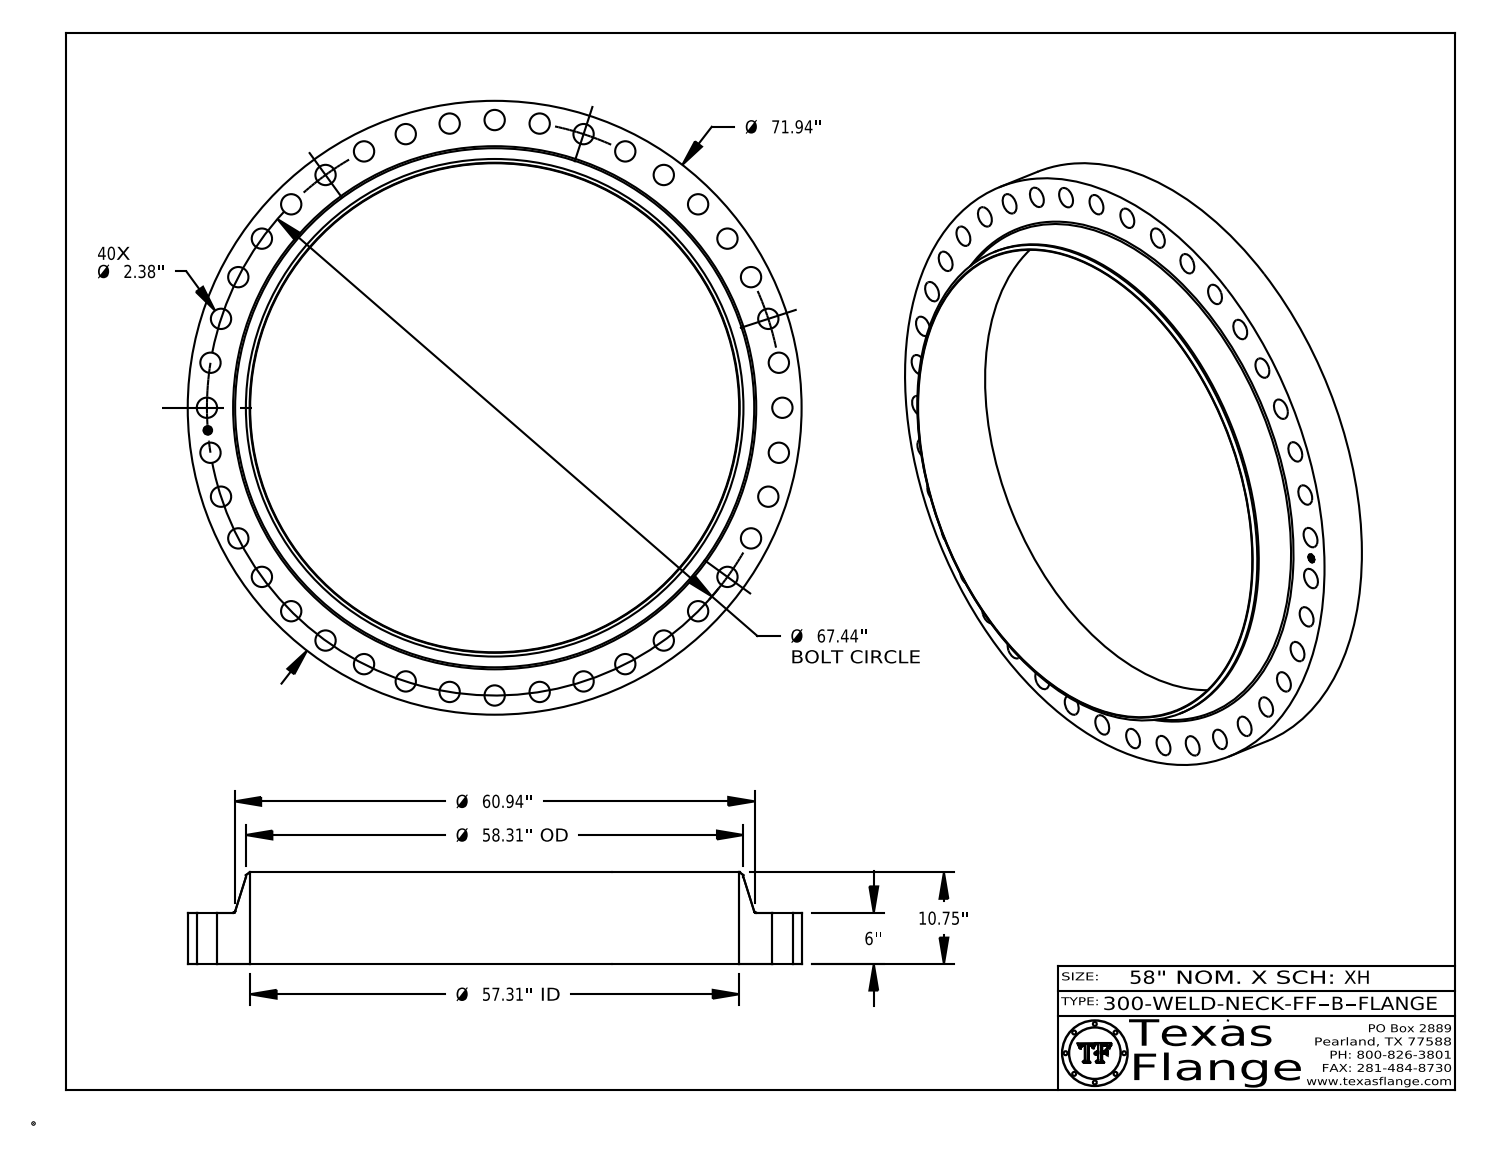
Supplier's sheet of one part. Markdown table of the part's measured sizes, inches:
| quantity | value |
| --- | --- |
| part name | 300-WELD-NECK-FF, Series B |
| STEP written by | CATIA V5 STEP AP214 (AUTOMOTIVE_DESIGN) |
| units | inches |
| bodies | 1 solid, 480 faces (368 planar, 106 cylindrical, 6 other) |
| overall size | 71.94 × 71.94 × 10.75 |
| volume | 8 773 in³ |
| surface area | 8 329 in² |
| round holes (diameter × count) | 2.38 × 40, 1 × 1, 57.31 × 1 |
| round bosses / shafts (diameter × count) | 0.061 × 8, 71.94 × 1, 58.31 × 1, 0.788 × 1 |
| main face-to-face distances | 6, 10.75, 4.75, 5.985, 0.015, 4.765, 0.298, 0.293, 0.054, 0.193 |
| hole center spacings | 10.55, 5.291, 20.84, 33.72, 65.577, 15.744, 25.808, 35.237 |
